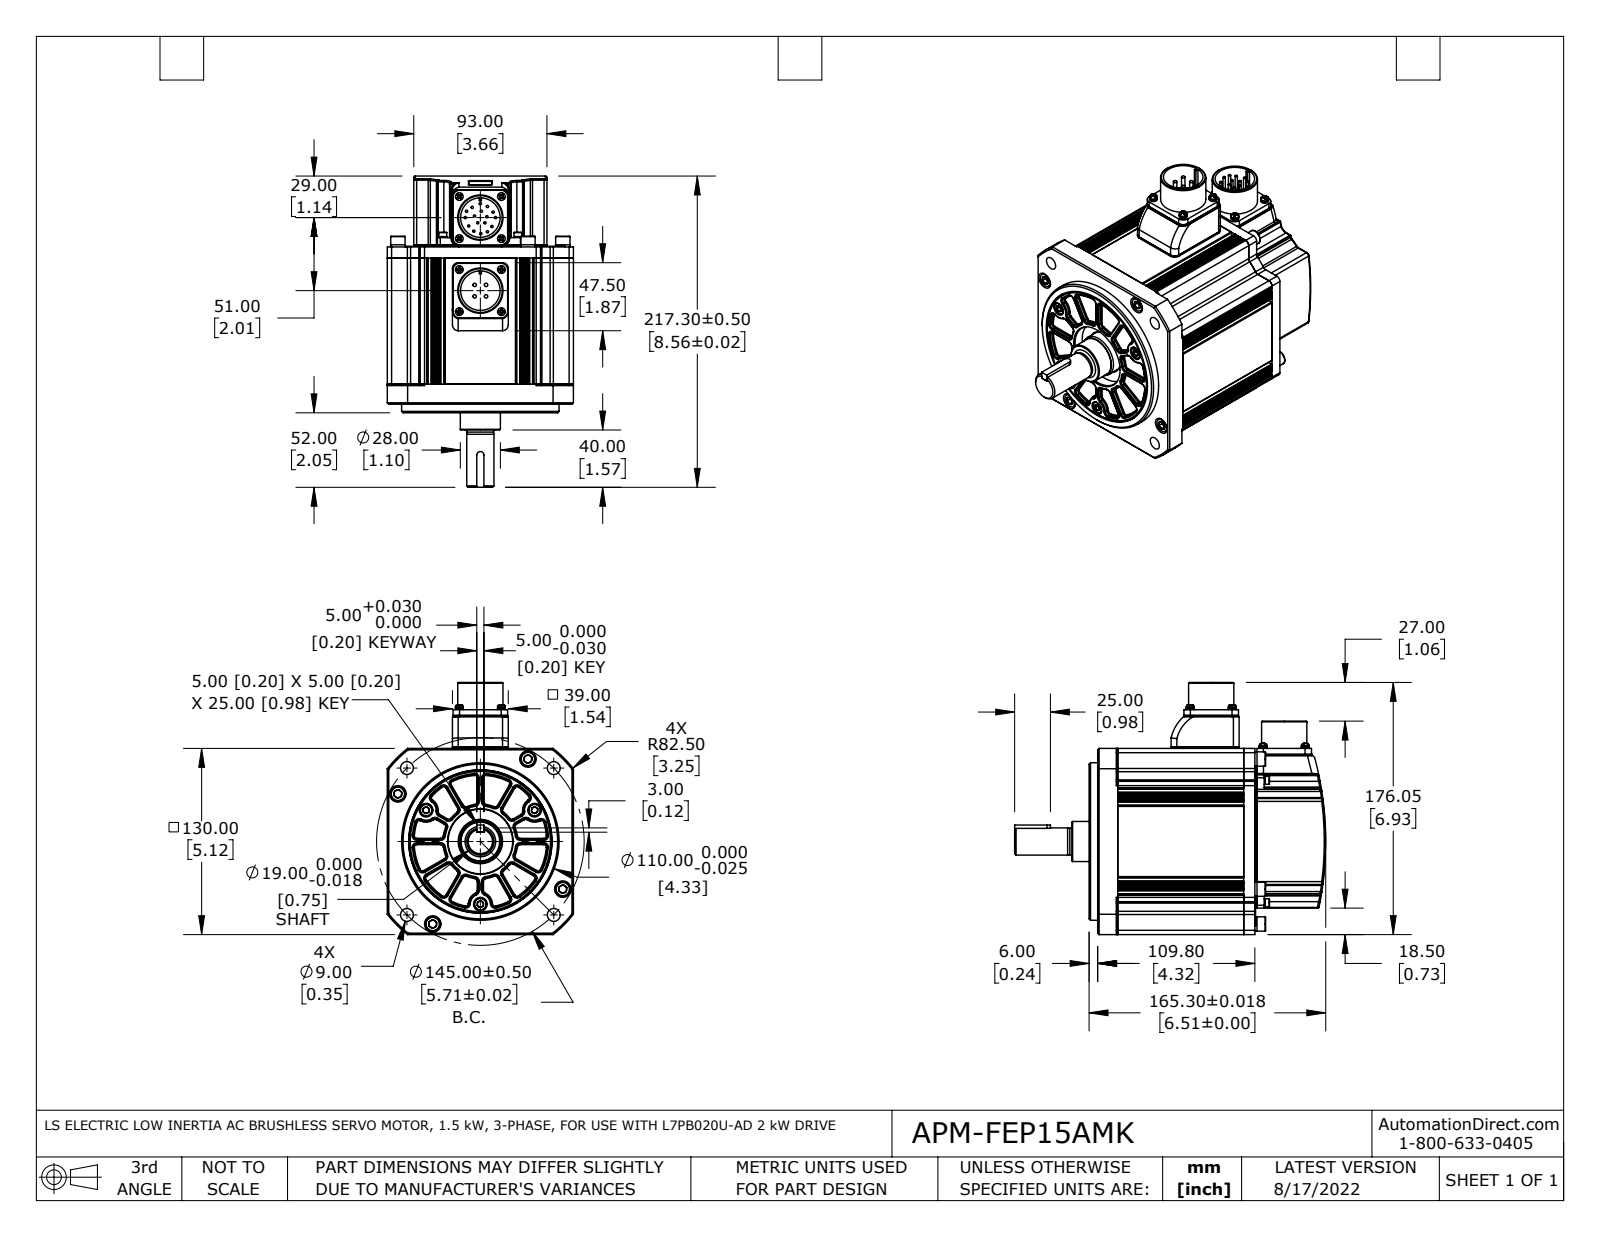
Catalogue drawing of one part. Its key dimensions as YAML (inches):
part_name: "FMP13GA001G02_Out Line(APM-FEP15A_K) r1 nc fxt"
step_written_by: "SolidWorks 2017 (AUTOMOTIVE_DESIGN)"
units: inches
bodies: {solids: 56, faces: 2125, planar: 706, cylindrical: 799, other: 620}
overall_size: [8.555, 6.931, 5.118]
volume: 130.2
surface_area: 449
round_holes:
  - {diameter: 0.098, count: 12}
  - {diameter: 0.118, count: 8}
  - {diameter: 0.12, count: 8}
  - {diameter: 0.138, count: 8}
  - {diameter: 0.197, count: 7}
  - {diameter: 0.142, count: 4}
  - {diameter: 0.146, count: 4}
  - {diameter: 0.268, count: 4}
  - {diameter: 0.276, count: 4}
  - {diameter: 0.354, count: 4}
  - {diameter: 0.453, count: 4}
  - {diameter: 0.22, count: 3}
round_bosses_or_shafts:
  - {diameter: 0.063, count: 17}
  - {diameter: 0.213, count: 8}
  - {diameter: 0.402, count: 4}
  - {diameter: 0.394, count: 4}
  - {diameter: 0.236, count: 4}
  - {diameter: 0.217, count: 4}
  - {diameter: 0.118, count: 4}
  - {diameter: 0.094, count: 4}
partial_cylinders:
  - {radius: 0.02, count: 72}
  - {radius: 0.098, count: 55}
  - {radius: 0.028, count: 24}
  - {radius: 0.079, count: 17}
  - {radius: 0.118, count: 16}
  - {radius: 0.039, count: 14}
  - {radius: 0.177, count: 12}
  - {radius: 0.157, count: 8}
face_to_face_distances: [3.465, 0.039, 3.831, 0.327, 3.791, 0.366, 4.244, 4.205, 3.878, 0.413]
hole_center_spacings: [0.819, 1.157, 2.008, 0.752, 1.041, 1.542, 1.637, 1.975]
